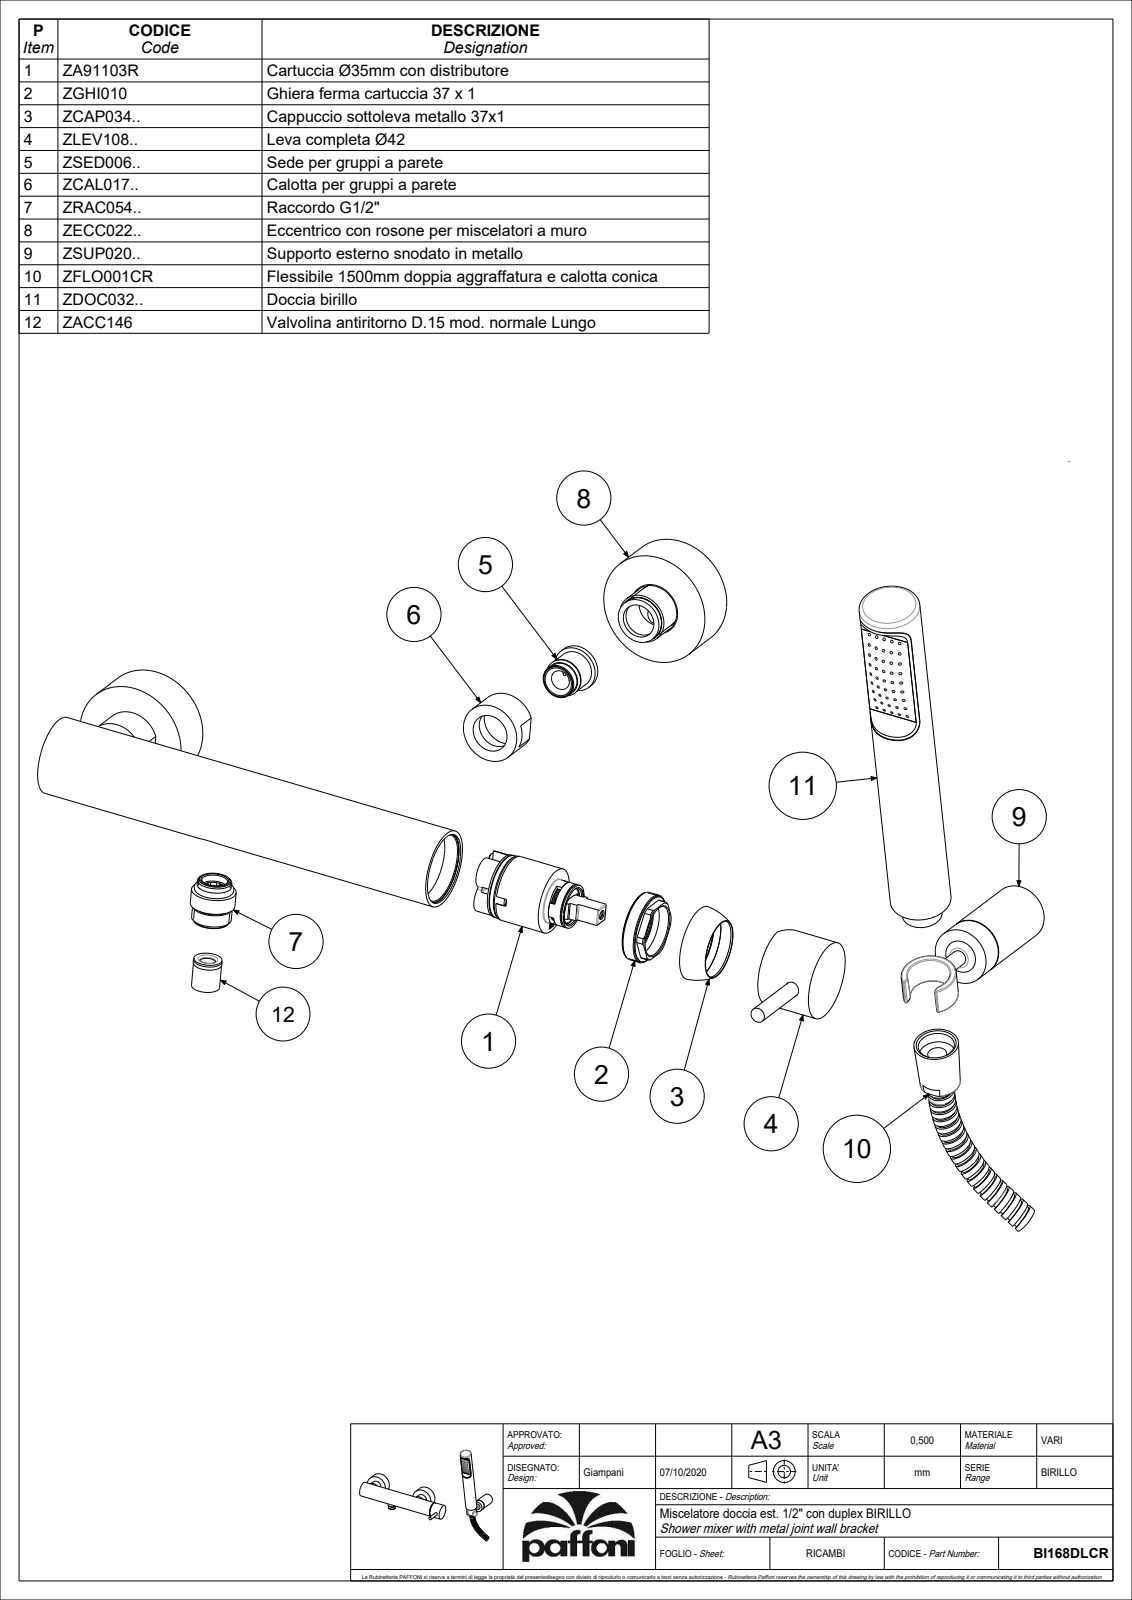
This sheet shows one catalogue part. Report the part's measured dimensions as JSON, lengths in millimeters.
{"part_name": "BI168DLCR", "step_written_by": "CREO PARAMETRIC BY PTC INC, 2020044 (CONFIG_CONTROL_DESIGN)", "units": "millimeters", "bodies": {"solids": 3, "faces": 1176, "planar": 504, "cylindrical": 397, "other": 275}, "overall_size": [427.84, 315.89, 192.38], "volume_mm3": 468219, "surface_area_mm2": 182340, "round_holes": [[1.5, 45], [7.5, 6], [8, 3], [9, 3], [12, 3], [16.7, 3], [4, 2], [5, 2], [10.5, 2], [18, 2], [20, 2], [24.5, 2]], "round_bosses_or_shafts": [[59.5, 2], [41.5, 2], [31.5, 2], [24, 2], [23.5, 2], [19.7, 2], [35, 1], [34.8, 1]], "partial_cylinders_radius": [[0.5, 54], [0.15, 11], [0.3, 9], [1, 4], [7, 4], [4.5, 2], [7.8, 2], [7.95, 2]], "face_to_face_distances": [4.7, 20, 24.7, 10, 18, 3, 42.7, 22.7, 2, 13], "hole_center_spacings": [7.91, 13.76, 6.5, 4.5, 11.1, 13, 20.01, 26.38]}
